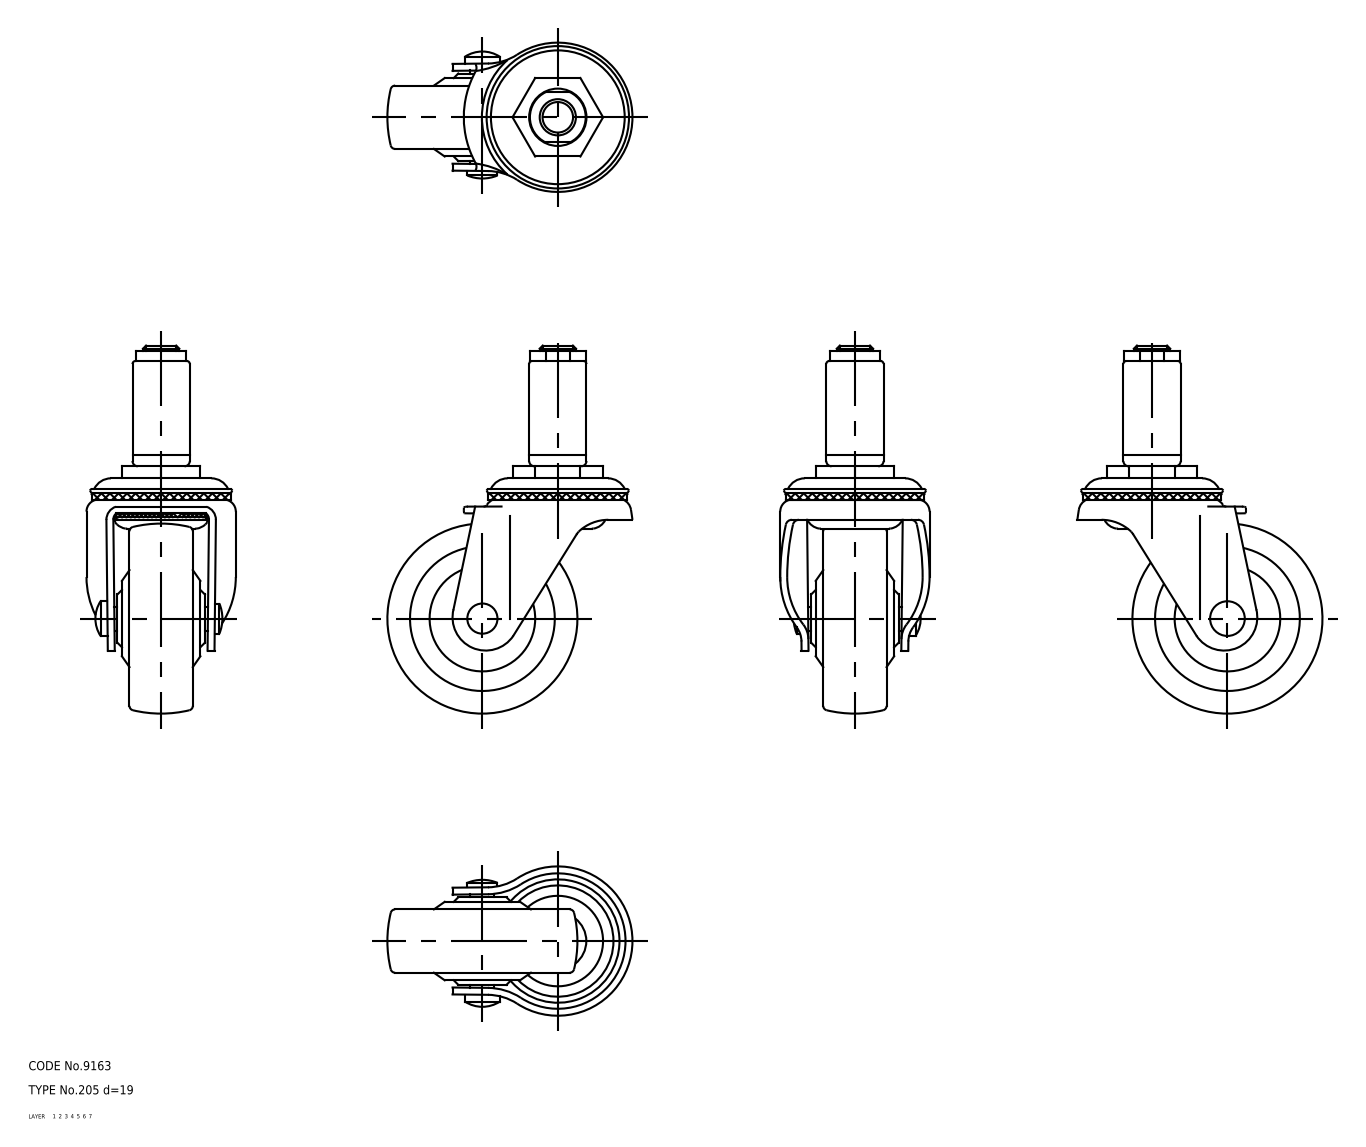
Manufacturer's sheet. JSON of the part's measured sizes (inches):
{"part_name": "wheel; main shaft; axle; No_205_d19_21467_36", "step_written_by": "CADfix (AUTOMOTIVE_DESIGN)", "units": "inches", "bodies": {"solids": 4, "faces": 212, "planar": 0, "cylindrical": 0, "other": 212}, "overall_size": [4.803, 3.199, 1.949], "volume_in3": 6.345, "surface_area_in2": 47.42}
